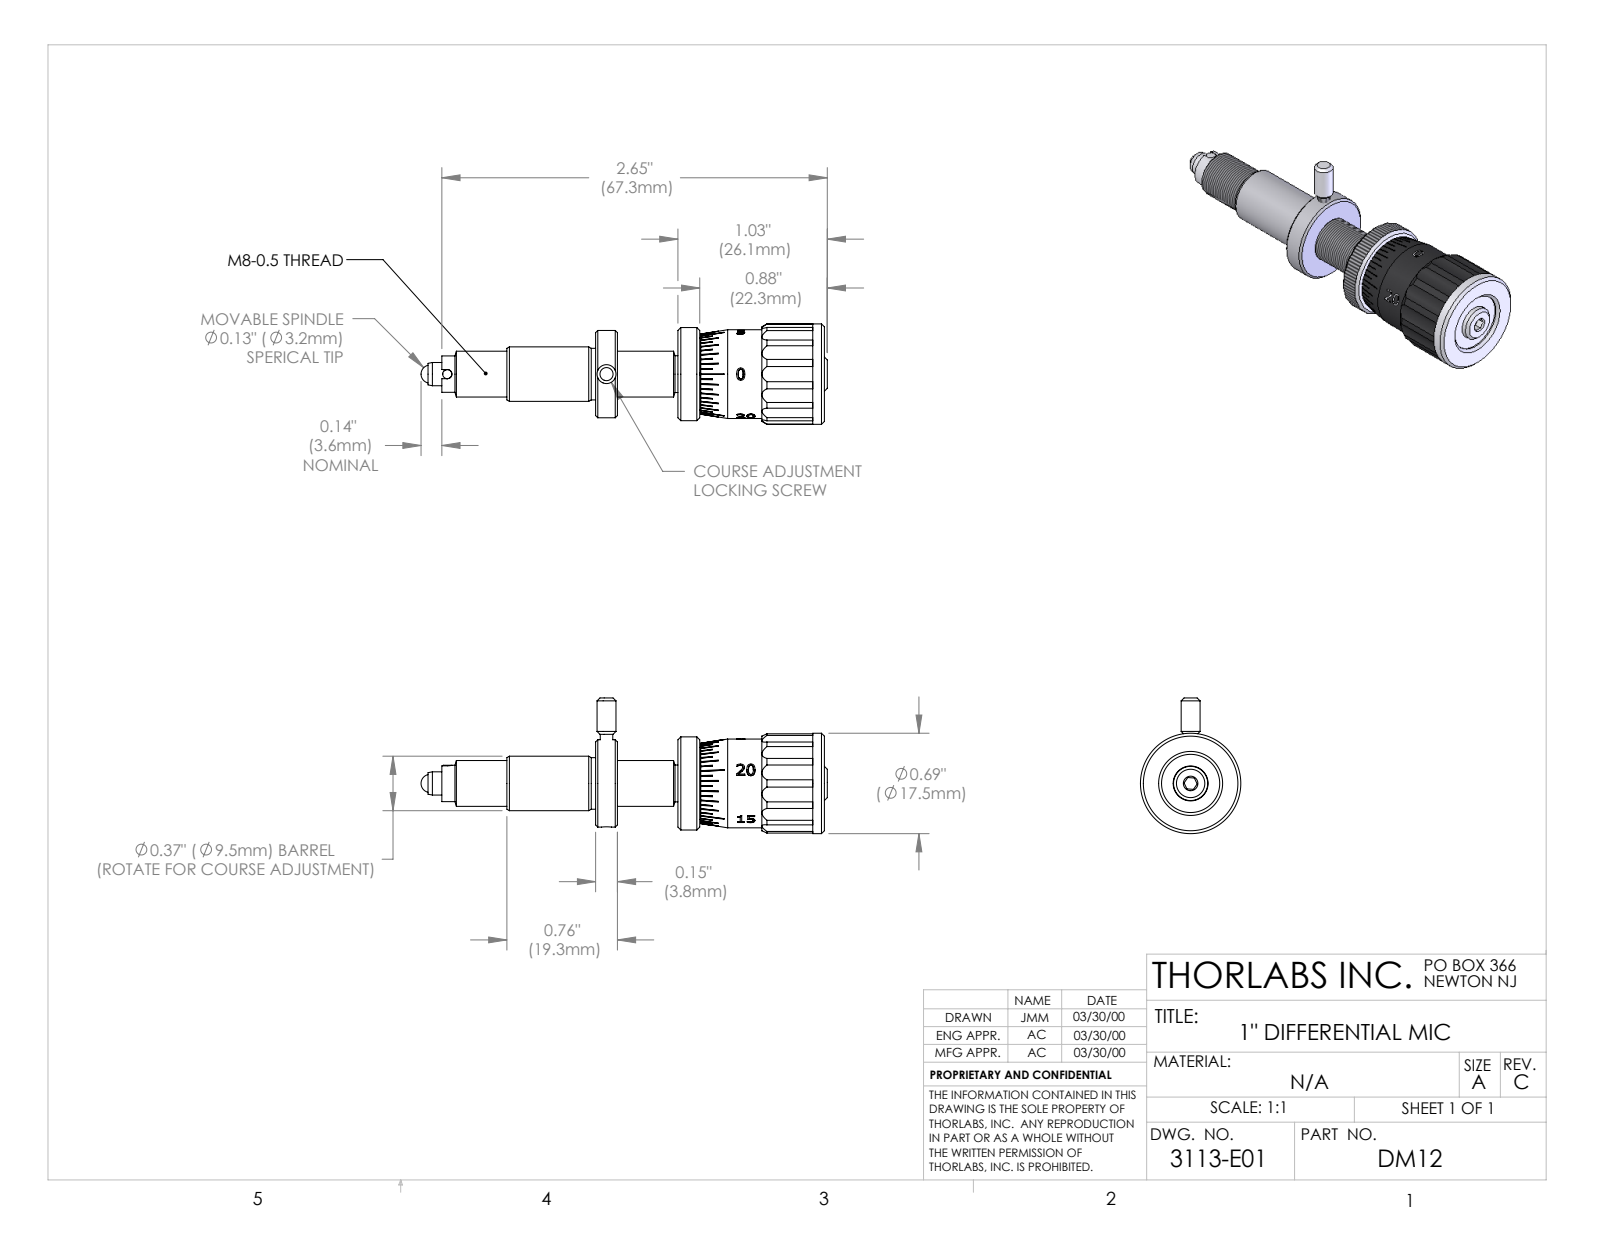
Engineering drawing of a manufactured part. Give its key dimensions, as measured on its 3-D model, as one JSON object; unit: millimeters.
{"part_name": "3113-E0W", "step_written_by": "SolidWorks 2007 (AUTOMOTIVE_DESIGN)", "units": "millimeters", "bodies": {"solids": 12, "faces": 610, "planar": 272, "cylindrical": 146, "other": 192}, "overall_size": [70.94, 23.68, 17.53], "volume_mm3": 7581, "surface_area_mm2": 9819, "round_holes": [[1.52, 1], [1.6, 1], [1.78, 1], [3.17, 1], [3.5, 1], [3.51, 1], [3.56, 1], [4.06, 1], [4.32, 1], [4.76, 1], [6, 1], [6.1, 1]], "round_bosses_or_shafts": [[2.18, 2], [17.53, 1], [16.26, 1], [15.49, 1], [15.24, 1], [12.57, 1], [12.55, 1], [11.18, 1]], "partial_cylinders_radius": [[2.38, 14], [0.8, 1], [7.76, 1]], "face_to_face_distances": [3.81, 14.37, 7.24, 2.03, 16.31, 23.55, 25.58, 9.27, 10.56, 26.87], "hole_center_spacings": [27.82]}
